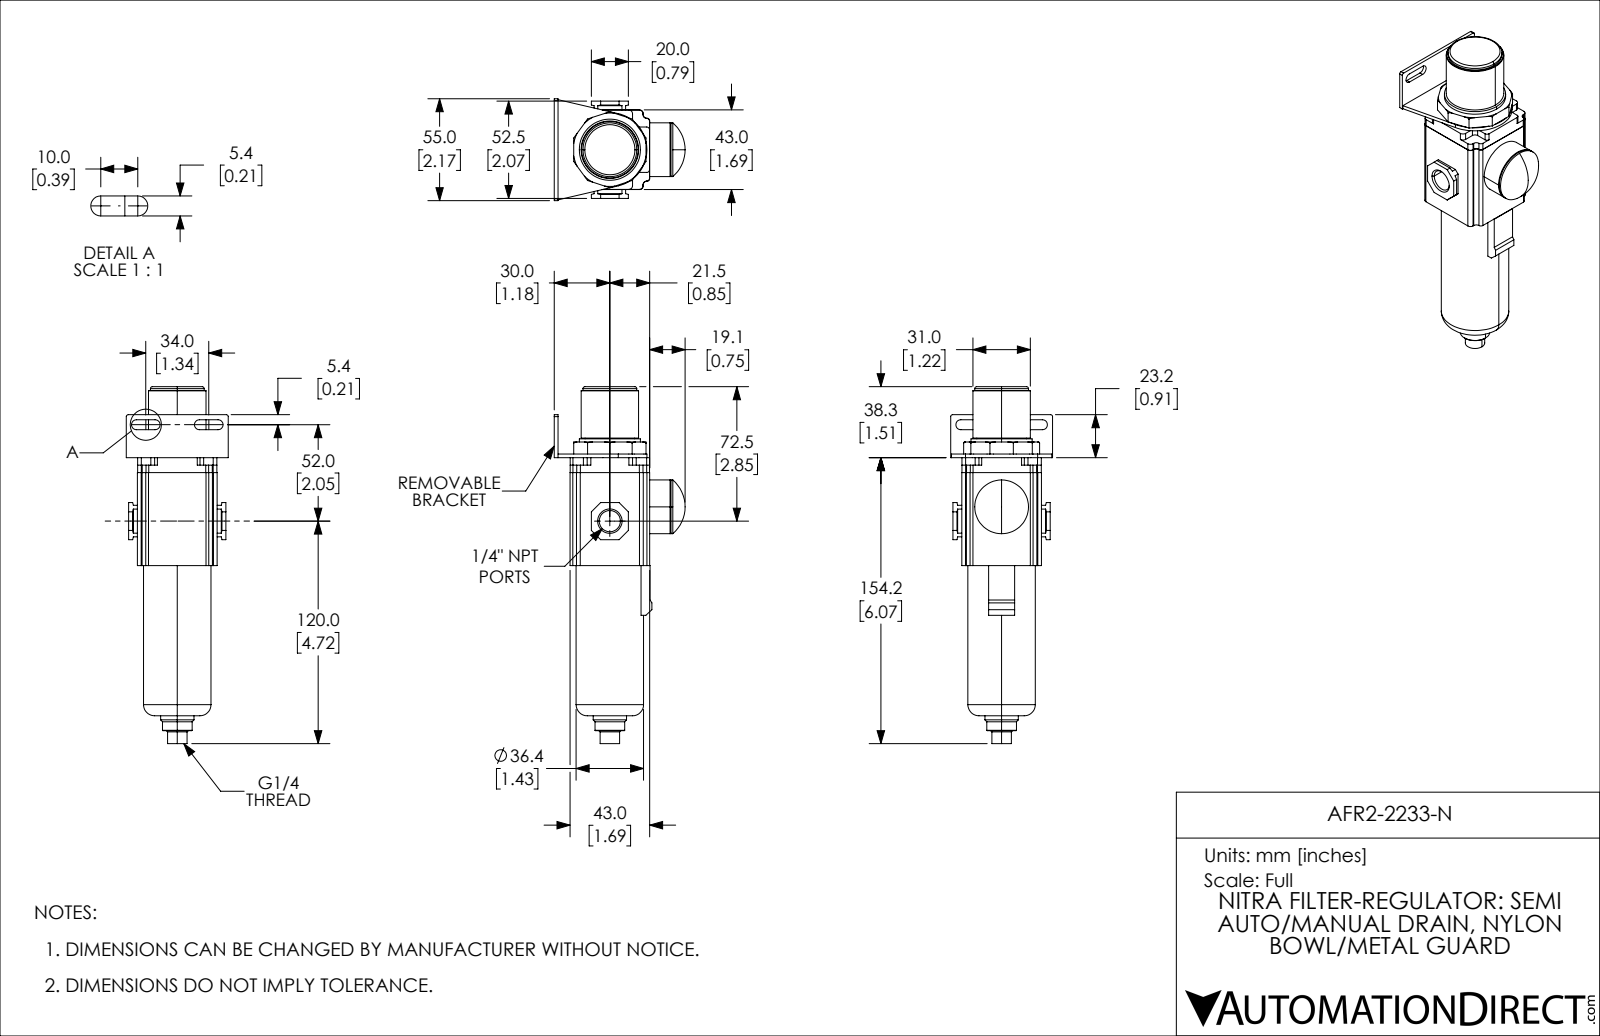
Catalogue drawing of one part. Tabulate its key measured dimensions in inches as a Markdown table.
| quantity | value |
| --- | --- |
| part name | AFR2-2233-N |
| STEP written by | SolidWorks 2019 (CONFIG_CONTROL_DESIGN) |
| units | inches |
| bodies | 1 solid, 220 faces (119 planar, 69 cylindrical, 32 other) |
| overall size | 7.579 × 2.78 × 2.165 |
| volume | 14.48 in³ |
| surface area | 52.86 in² |
| round holes (diameter × count) | 0.163 × 1, 0.451 × 1 |
| round bosses / shafts (diameter × count) | 1.142 × 2, 1.433 × 1, 1.299 × 1, 1.22 × 1, 1.054 × 1, 0.709 × 1, 0.63 × 1, 0.413 × 1 |
| partial cylindrical surfaces (radius × count) | 0.079 × 24, 0.059 × 12, 0.106 × 4, 0.039 × 2, 0.787 × 1 |
| main face-to-face distances | 1.693, 0.079, 0.335, 0.256, 1.949, 2.028, 1.689, 1.429, 2.291, 2.37 |
